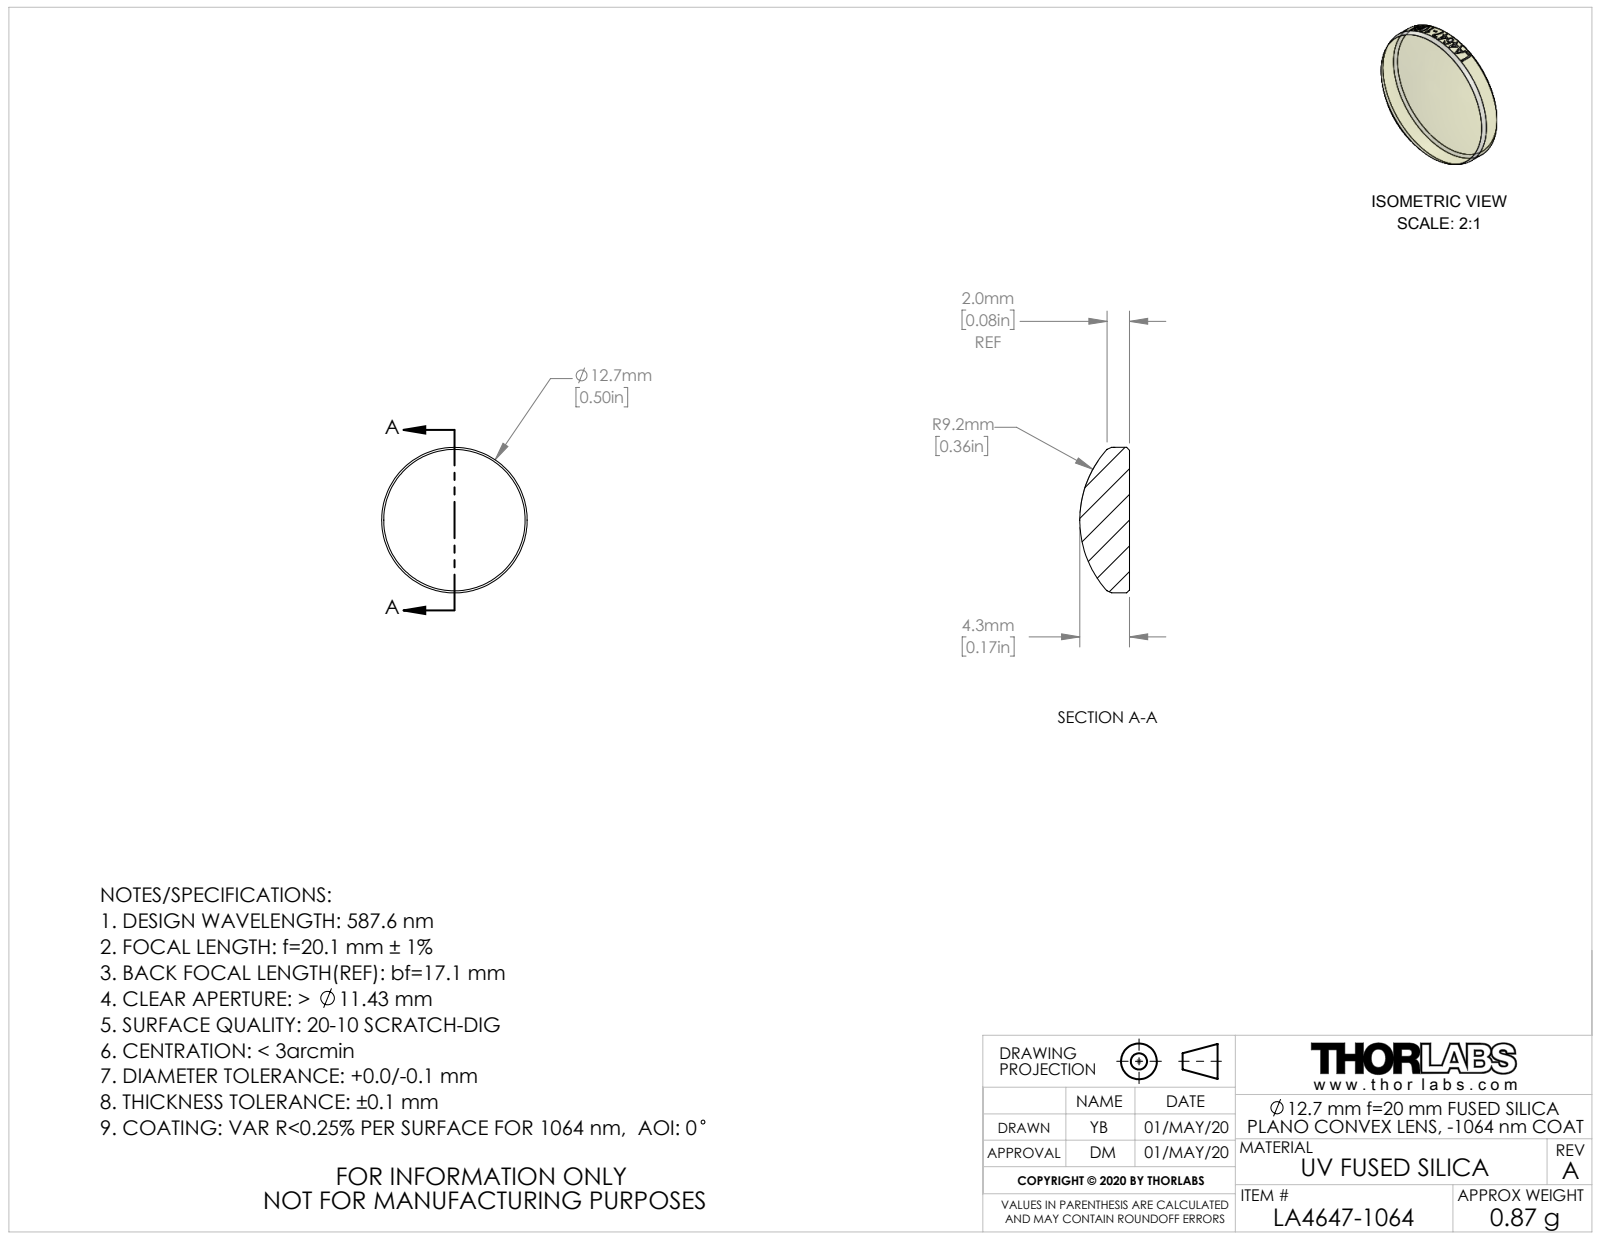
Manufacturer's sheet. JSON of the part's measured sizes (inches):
{"part_name": "CTN015558-E0W", "step_written_by": "SolidWorks 2018 (AUTOMOTIVE_DESIGN)", "units": "inches", "bodies": {"solids": 1, "faces": 27, "planar": 1, "cylindrical": 20, "other": 6}, "overall_size": [0.5, 0.5, 0.171], "volume_in3": 0.024, "surface_area_in2": 0.524, "round_bosses_or_shafts": [[0.5, 1]]}
